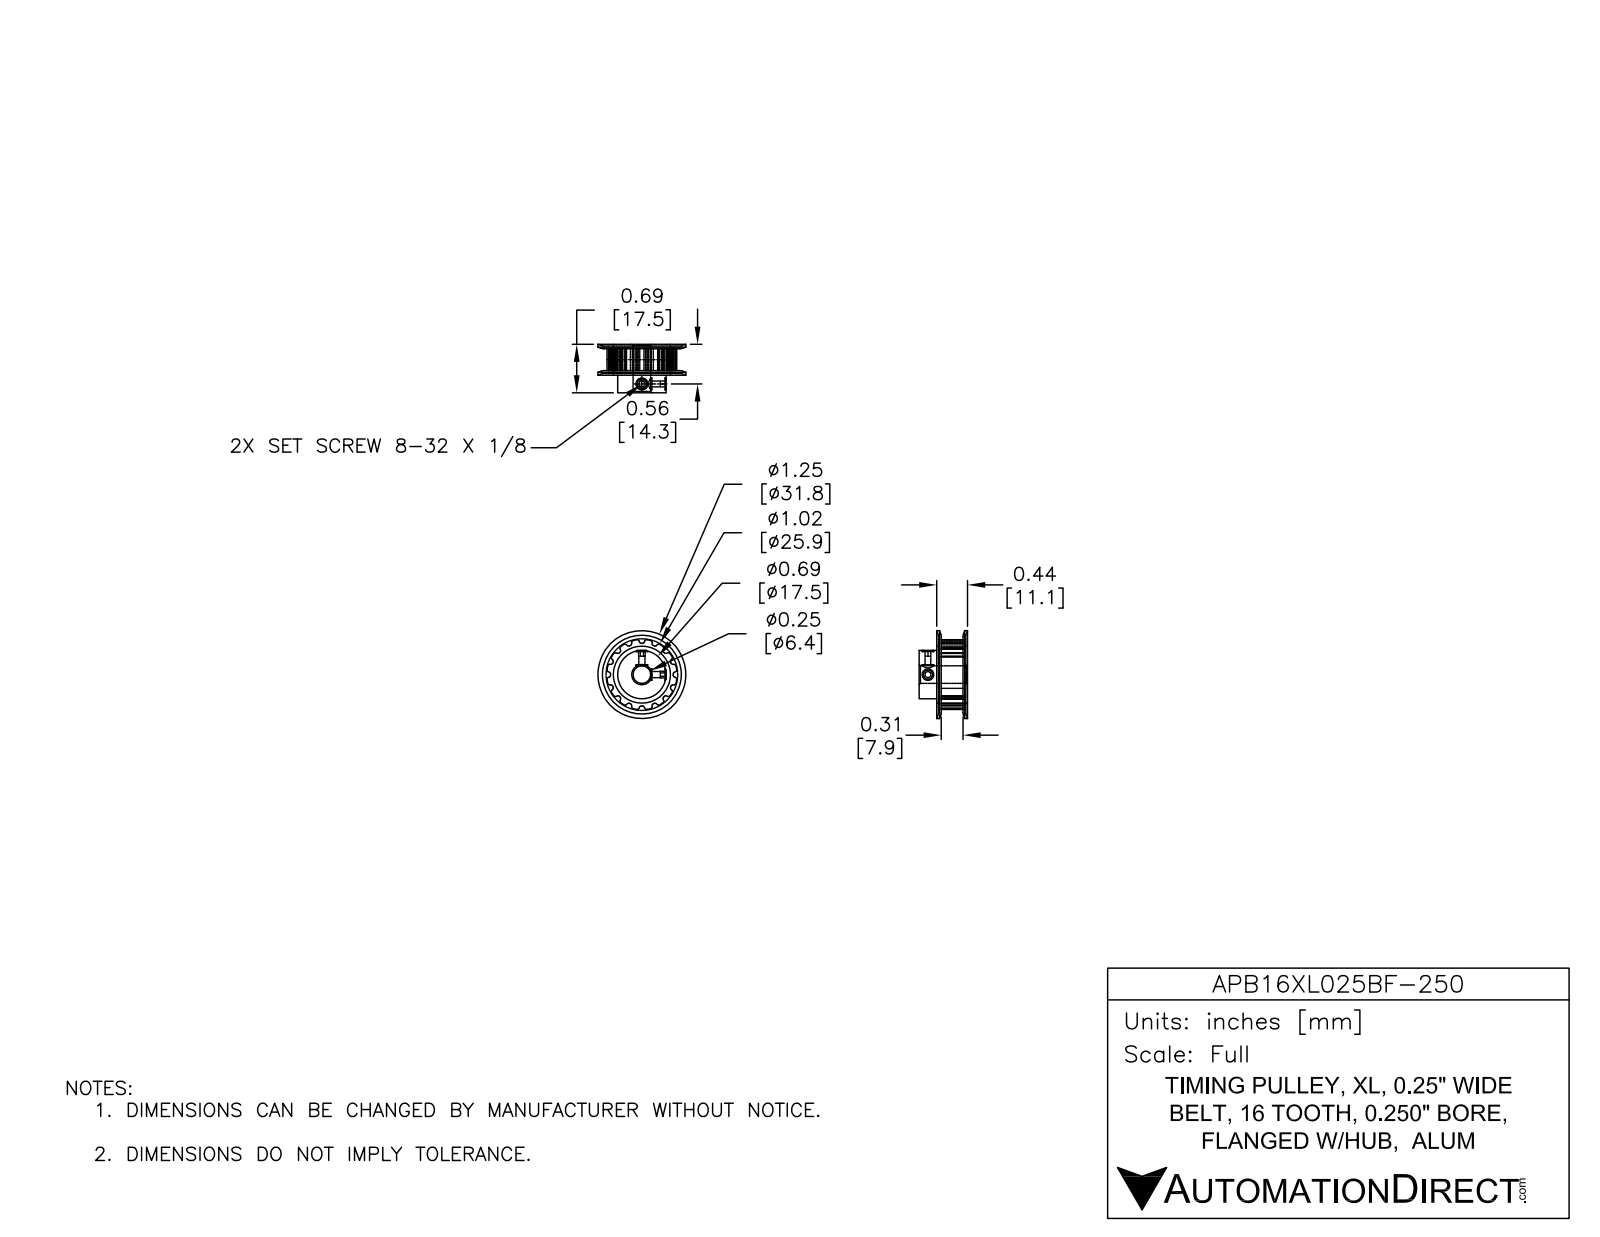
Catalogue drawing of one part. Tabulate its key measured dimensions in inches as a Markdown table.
| quantity | value |
| --- | --- |
| part name | APB16XL025BF-250 |
| STEP written by | SolidWorks 2014 (AUTOMOTIVE_DESIGN) |
| units | inches |
| bodies | 1 solid, 178 faces (54 planar, 102 cylindrical, 22 other) |
| overall size | 1.25 × 1.25 × 0.688 |
| volume | 0.382 in³ |
| surface area | 6.16 in² |
| round holes (diameter × count) | 0.088 × 2, 0.25 × 1 |
| round bosses / shafts (diameter × count) | 0.688 × 1 |
| partial cylindrical surfaces (radius × count) | 0.015 × 64, 0.444 × 1 |
| main face-to-face distances | 0.375, 0.033, 0.407, 0.688, 0.656, 0.281, 0.032, 0.343, 0.999, 0.329 |
